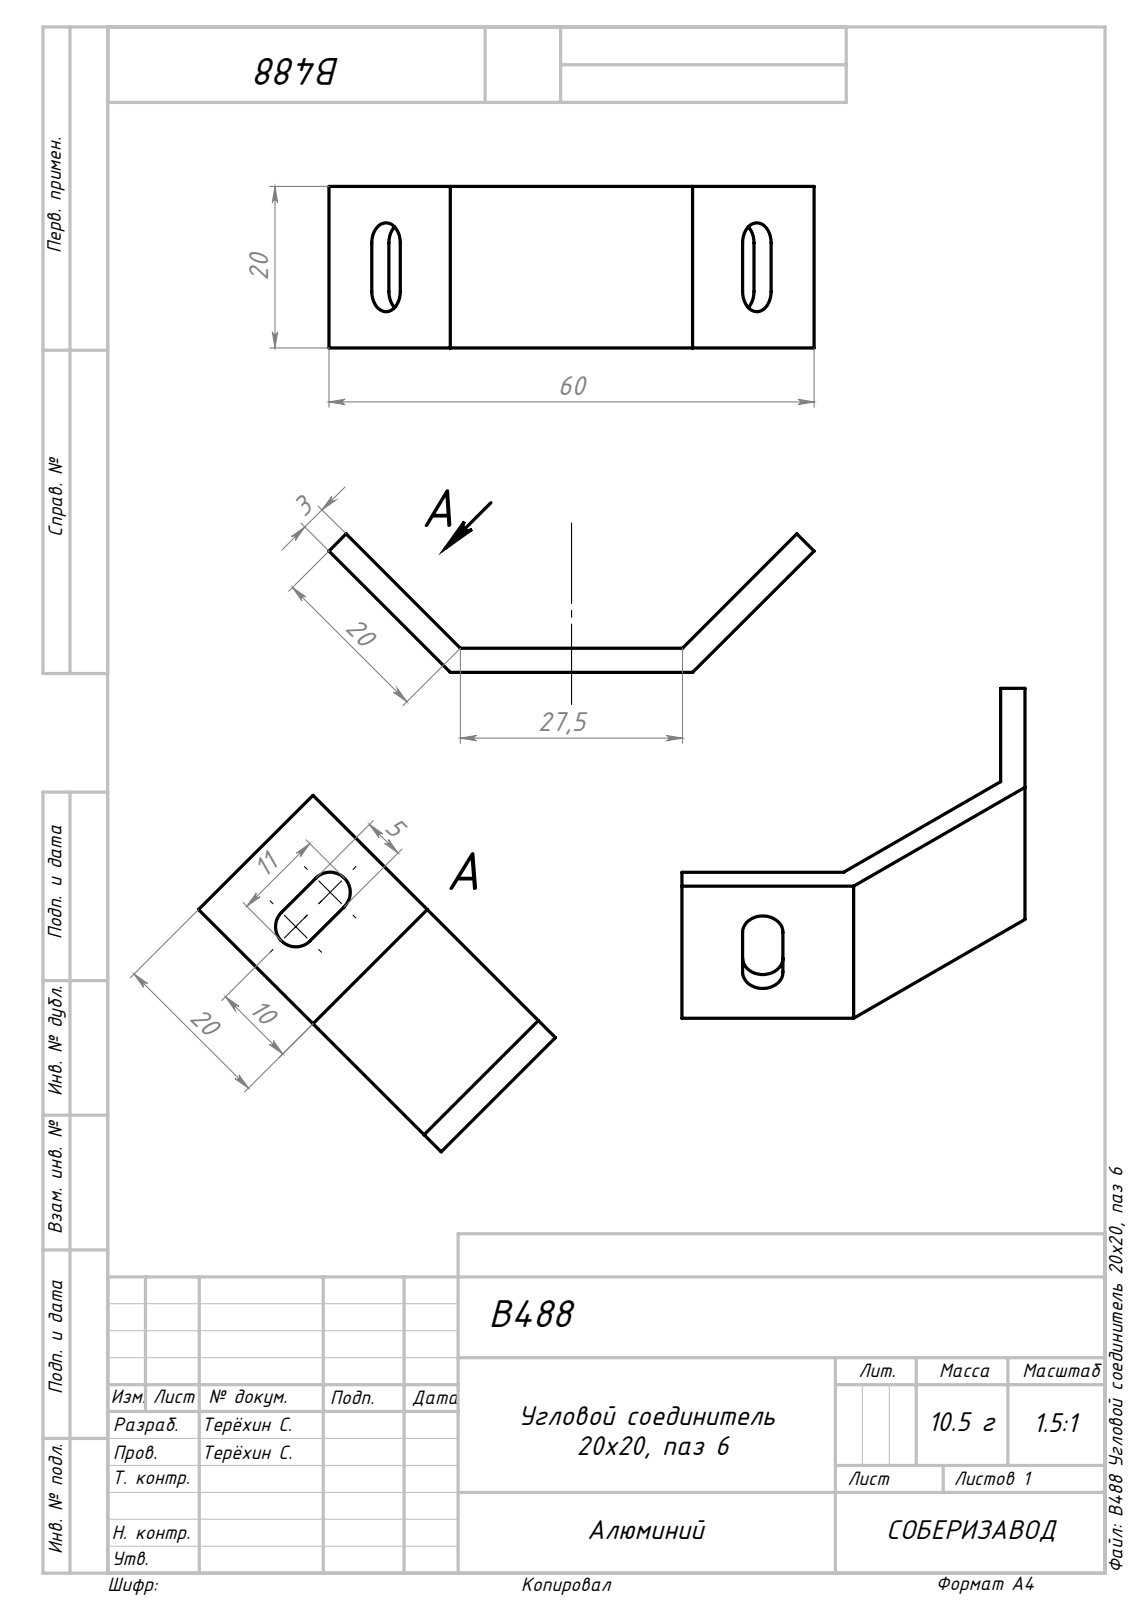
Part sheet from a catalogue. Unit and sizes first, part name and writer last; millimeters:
Units: millimetres
Overall size (bounding box): 60 × 20 × 17.14
Partial cylindrical surfaces — rounded edges, fillets, slot ends (radius × count): R2.5 ×4
Main face-to-face distances: 3, 20, 39.42, 42.42, 12.5, 26.92, 29.92, 7.5, 5, 31.92
Volume: 3 900 mm³ · Surface area: 3 306 mm²
Bodies: 1 solid, 18 faces (14 planar, 4 cylindrical, 0 other)
Part name (STEP PRODUCT): B488 Угловой соединитель 20x20, паз 6_00; Сборка1
STEP written by: SolidWorks 2022 (AUTOMOTIVE_DESIGN)
